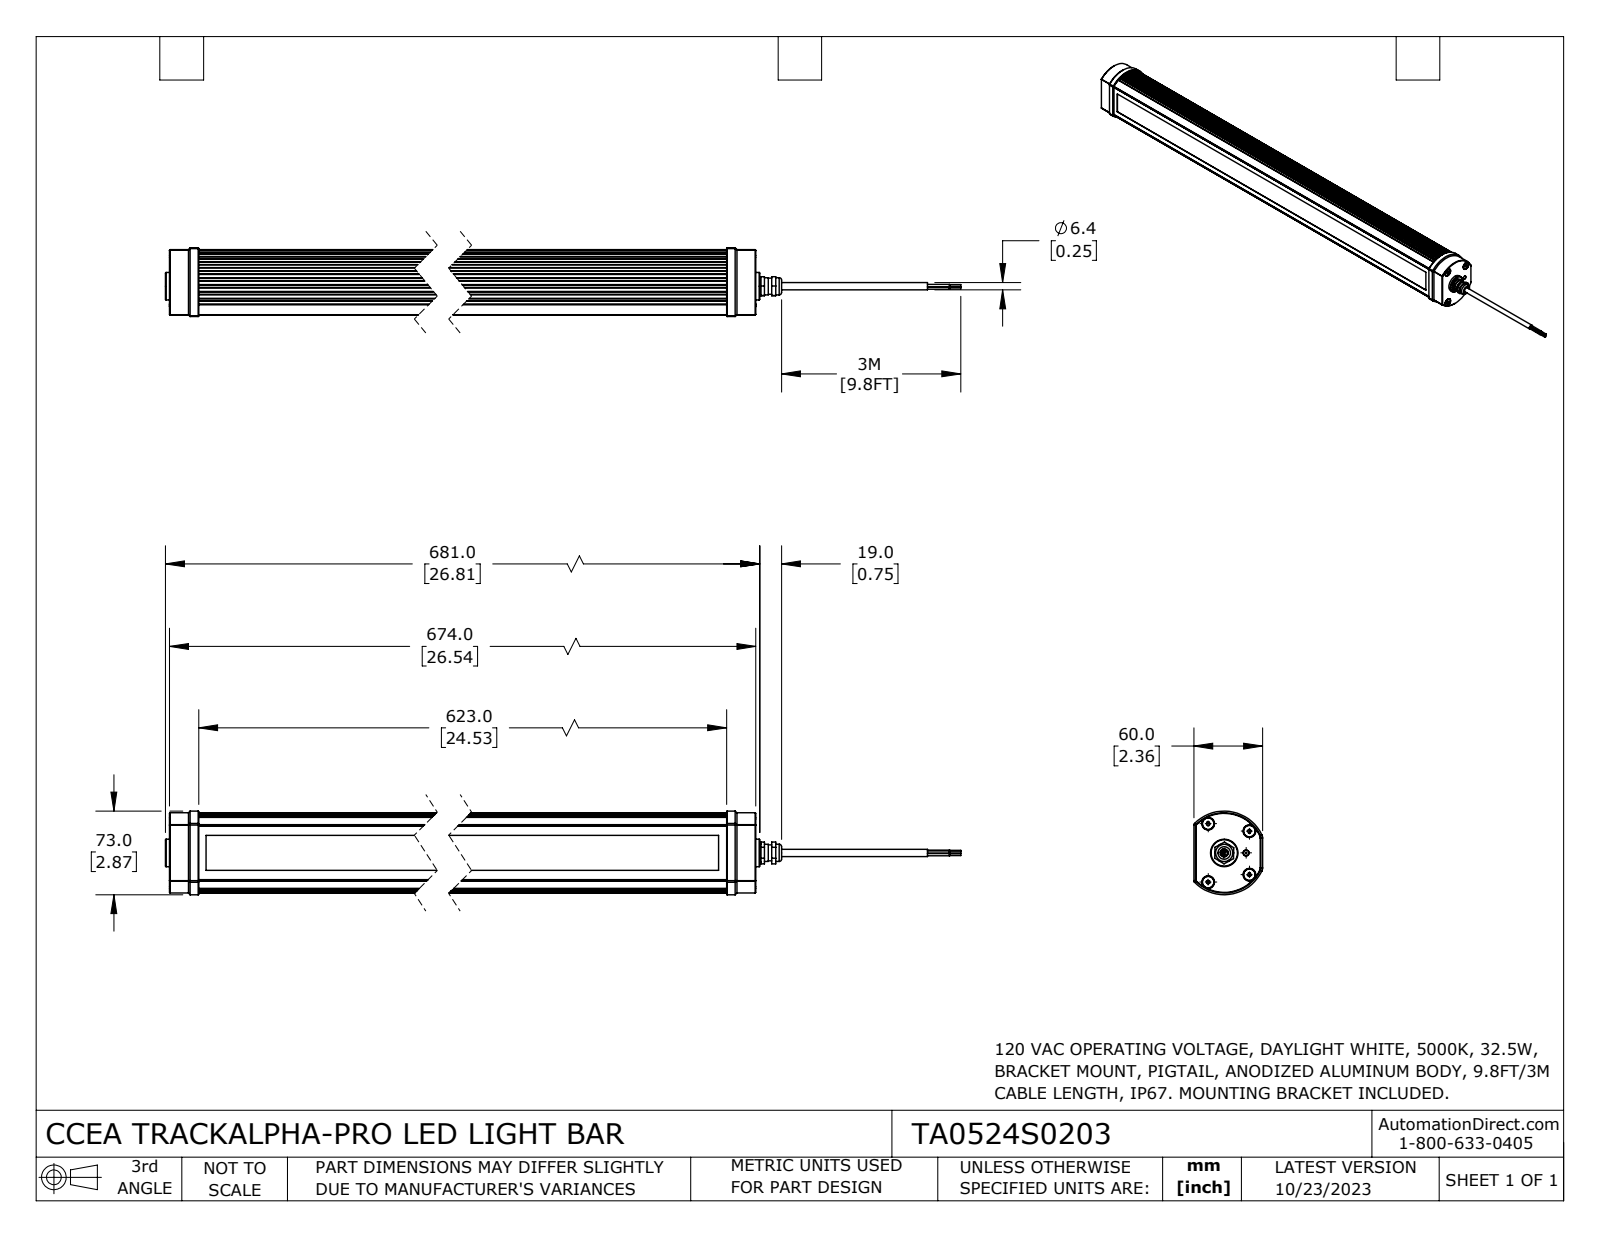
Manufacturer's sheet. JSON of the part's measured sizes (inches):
{"part_name": "TA0524S0203", "step_written_by": "SolidWorks 2023 (CONFIG_CONTROL_DESIGN)", "units": "inches", "bodies": {"solids": 19, "faces": 625, "planar": 196, "cylindrical": 279, "other": 150}, "overall_size": [33.72, 2.874, 2.362], "volume_in3": 138, "surface_area_in2": 458.6, "round_holes": [[0.217, 4], [0.043, 3], [0.12, 2], [0.394, 2], [0.194, 1], [0.276, 1], [0.551, 1], [1.063, 1]], "round_bosses_or_shafts": [[0.394, 4], [0.197, 4], [0.067, 3], [0.063, 3], [0.039, 3], [0.082, 2], [0.945, 1], [0.591, 1]], "partial_cylinders_radius": [[0.02, 22], [0.012, 16], [0.059, 10], [0.073, 8], [0.079, 4], [0.197, 3], [0.039, 2], [0.217, 2]], "face_to_face_distances": [0.197, 0.02, 0.217, 2.024, 2.043, 2.24, 2.242, 0.219, 0.199, 1.841], "hole_center_spacings": [0.334, 0.505, 0.726, 0.757, 0.831, 0.948, 0.992, 1.144]}
